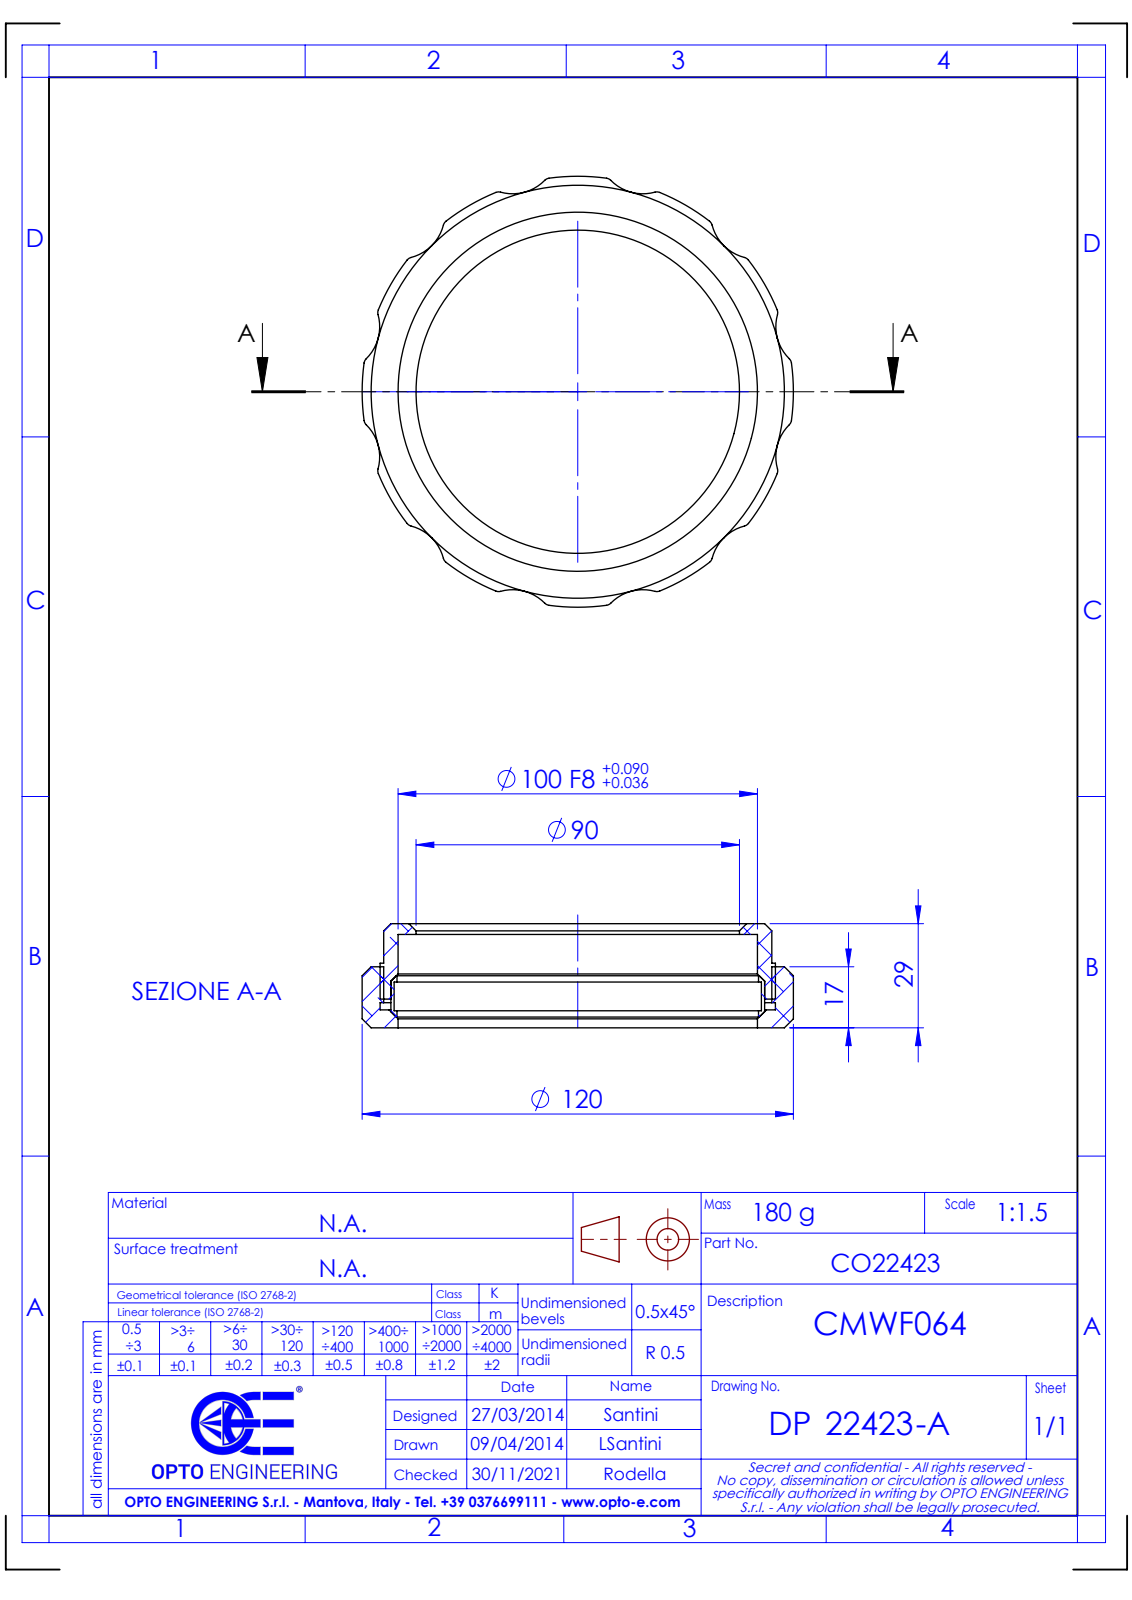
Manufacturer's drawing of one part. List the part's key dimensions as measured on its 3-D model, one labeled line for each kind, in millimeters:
Part name (STEP PRODUCT): DP22423 -A_CMWF064
STEP written by: SolidWorks 2021 (CONFIG_CONTROL_DESIGN)
Units: millimetres
Bodies: 0 solids, 140 faces (14 planar, 90 cylindrical, 36 other)
Overall size (bounding box): 119.05 × 119.05 × 29
Round holes (diameter × count): ⌀90 ×1, ⌀100 ×1, ⌀100.6 ×1, ⌀102.2 ×1, ⌀104 ×1, ⌀108 ×1
Round bosses / shafts (diameter × count): ⌀110 ×1
Partial cylindrical surfaces — rounded edges, fillets, slot ends (radius × count): R2 ×24, R12.5 ×12, R40 ×6, R60 ×1
Main face-to-face distances: 3, 9, 12, 21, 8, 29, 26, 18, 17, 5
